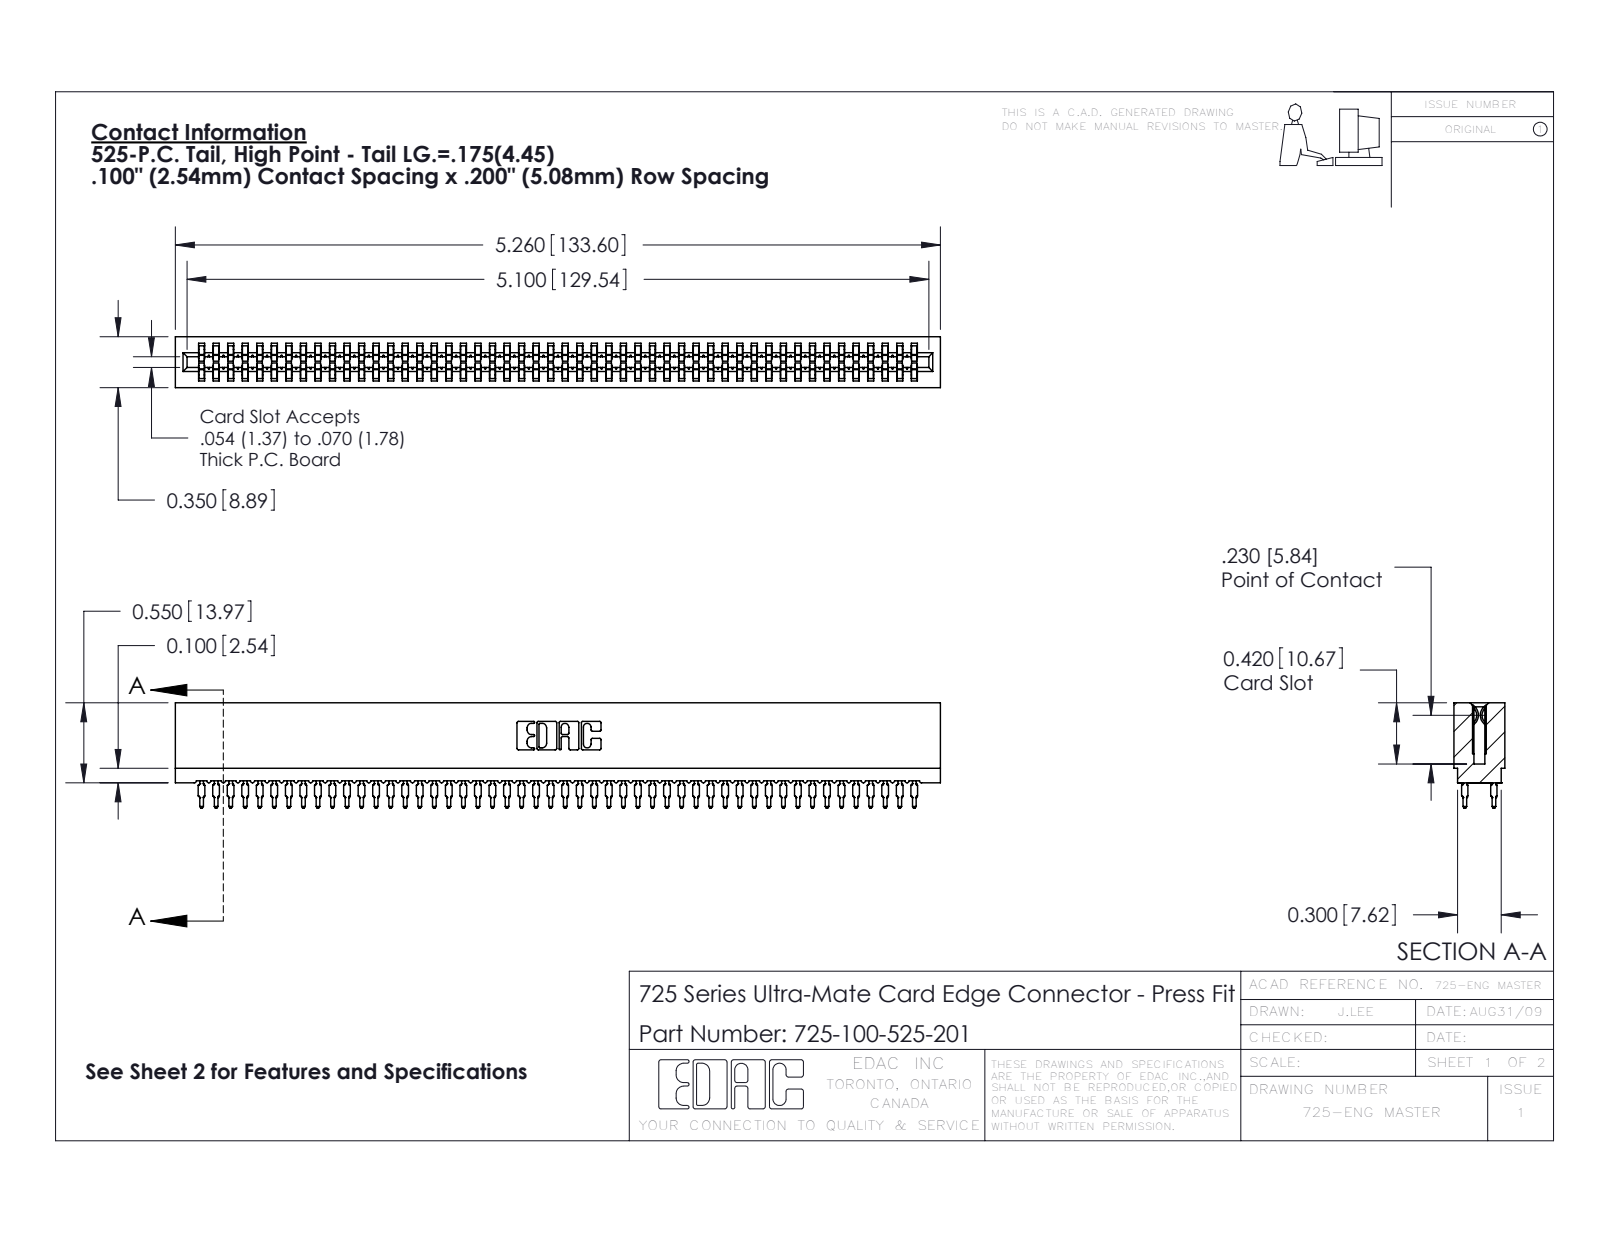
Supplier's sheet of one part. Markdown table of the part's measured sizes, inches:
| quantity | value |
| --- | --- |
| part name | 725-100-525-201; 745-292-001_525; 725 Part_Insulator Option - 01 |
| STEP written by | SolidWorks 2016 (CONFIG_CONTROL_DESIGN) |
| units | inches |
| bodies | 101 solids, 9045 faces (4655 planar, 1790 cylindrical, 2600 other) |
| overall size | 5.26 × 0.725 × 0.35 |
| volume | 0.641 in³ |
| surface area | 34.48 in² |
| partial cylindrical surfaces (radius × count) | 0.021 × 200, 0.015 × 100, 0.01 × 22, 0.005 × 8, 0.011 × 8, 0.007 × 6, 0.031 × 6, 0.026 × 3 |
| main face-to-face distances | 0.063, 0.287, 0.35, 0.212, 0.138, 0.076, 0.149, 0.305, 0.045, 0.018 |
